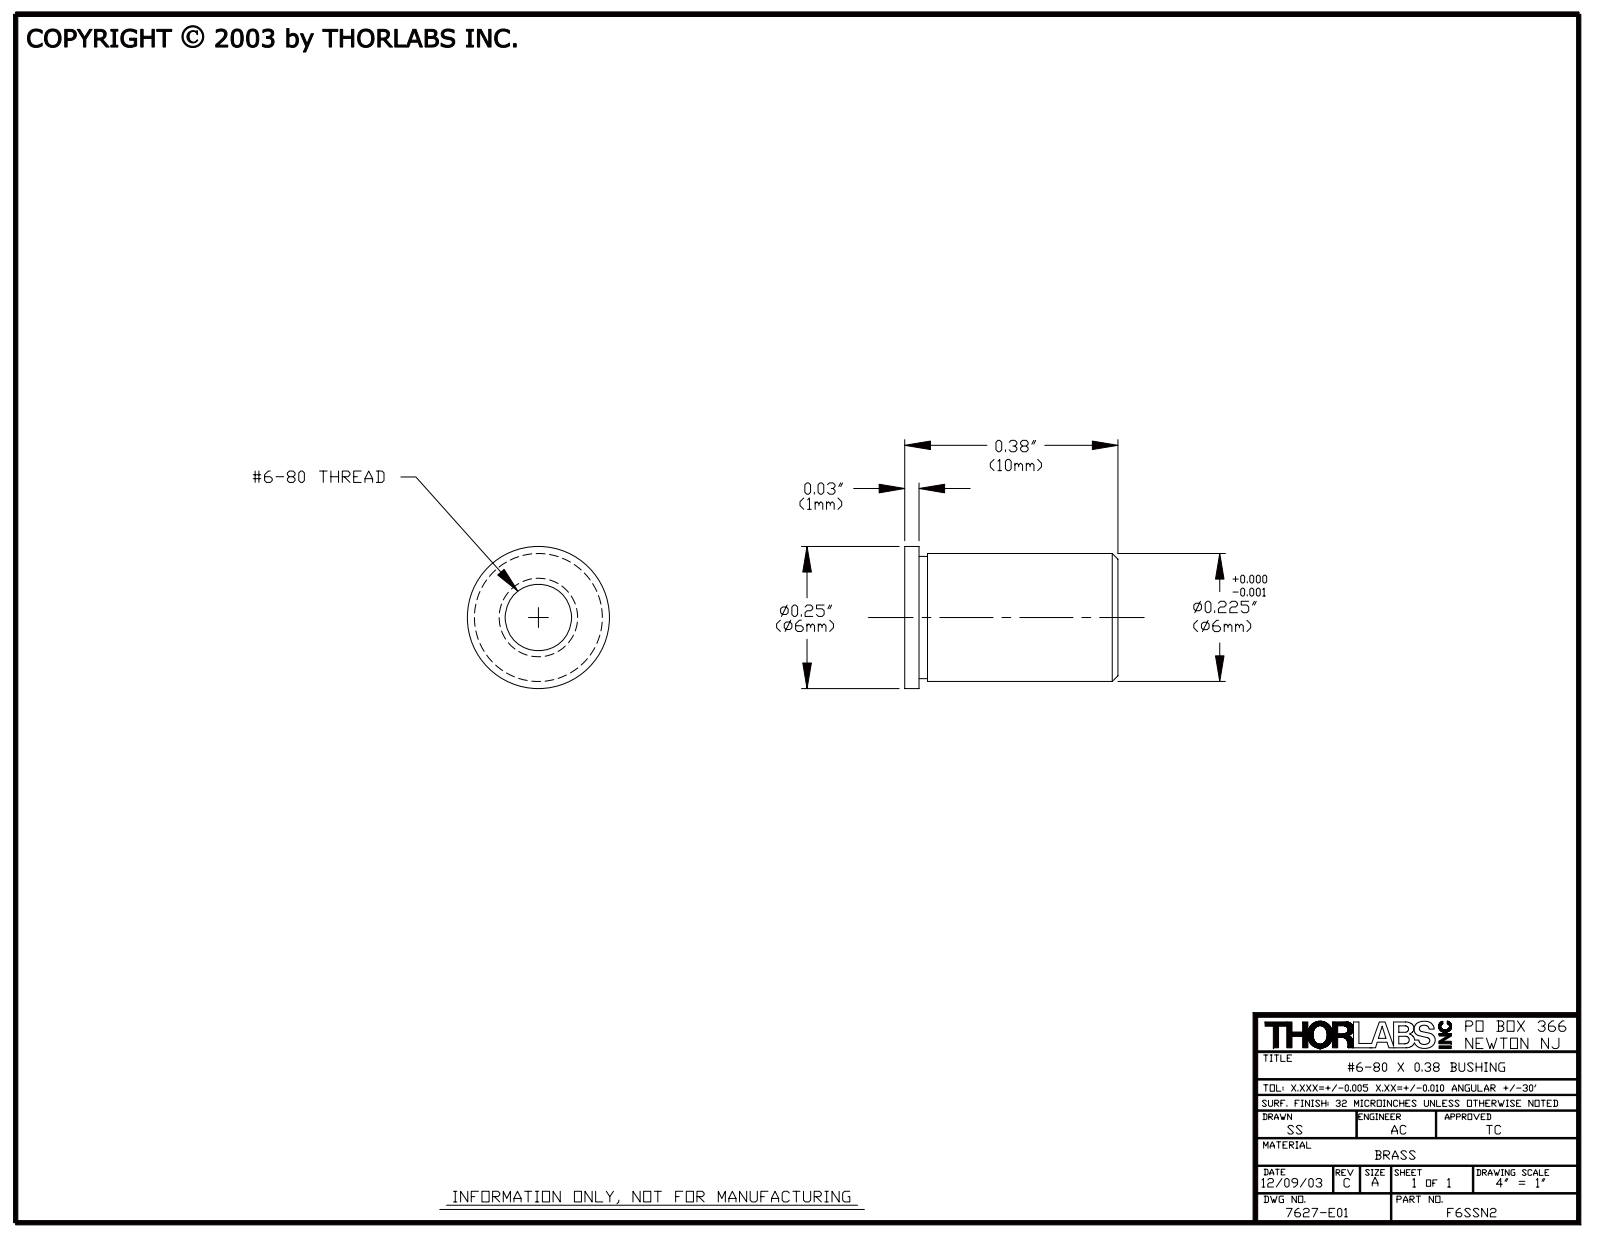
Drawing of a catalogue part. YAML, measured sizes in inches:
part_name: "7627-E0W"
step_written_by: "SolidWorks 2007 (AUTOMOTIVE_DESIGN)"
units: inches
bodies: {solids: 1, faces: 15, planar: 3, cylindrical: 6, other: 6}
overall_size: [0.375, 0.25, 0.25]
volume: 0.012
surface_area: 0.462
round_holes:
  - {diameter: 0.104, count: 1}
round_bosses_or_shafts:
  - {diameter: 0.25, count: 1}
  - {diameter: 0.225, count: 1}
face_to_face_distances: [0.375, 0.35, 0.025]
